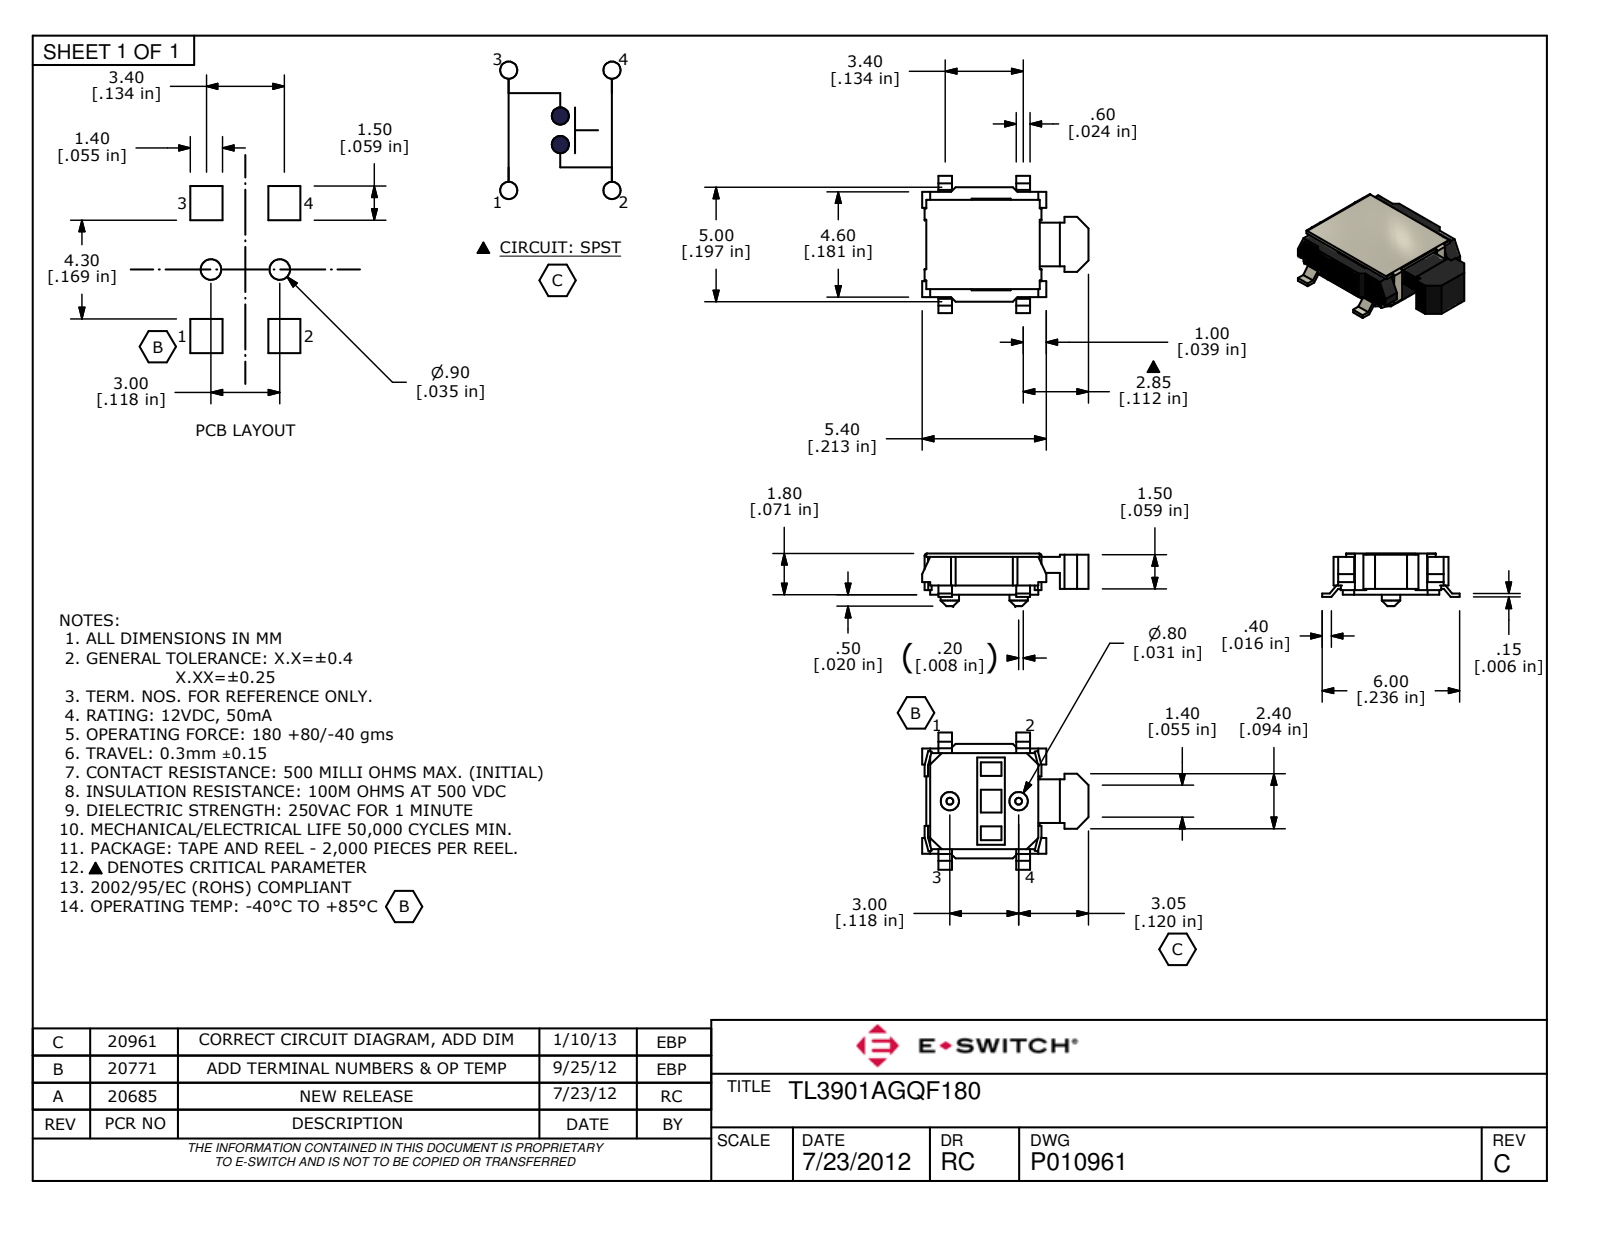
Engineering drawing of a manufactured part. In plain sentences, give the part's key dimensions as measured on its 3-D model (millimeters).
The part is named "P:\\\\E-Switch Secure\\\\3D_MODELS_STP_FORMAT\\\\TL3901AGQF180.stp". Its 3-D file was written by "ACIS (CONFIG_CONTROL_DESIGN)". It is 1 solid with 225 faces: 216 planar, 7 cylindrical and 2 other. Overall it measures 7.2 by 6 by 2.3 millimeters. Its volume is 30 cubic millimeters and its surface area 164 square millimeters. Round bosses or shafts: 2 of diameter 0.8. Partial cylindrical surfaces (rounded edges, fillets, slot ends): 2 of radius 0.1, 1 of radius 0.4. The main face-to-face distances are 0.9, 0.8, 0.8, 1.7, 0.4, 1.8, 0.7, 0.5, 0.9, 1.5.
